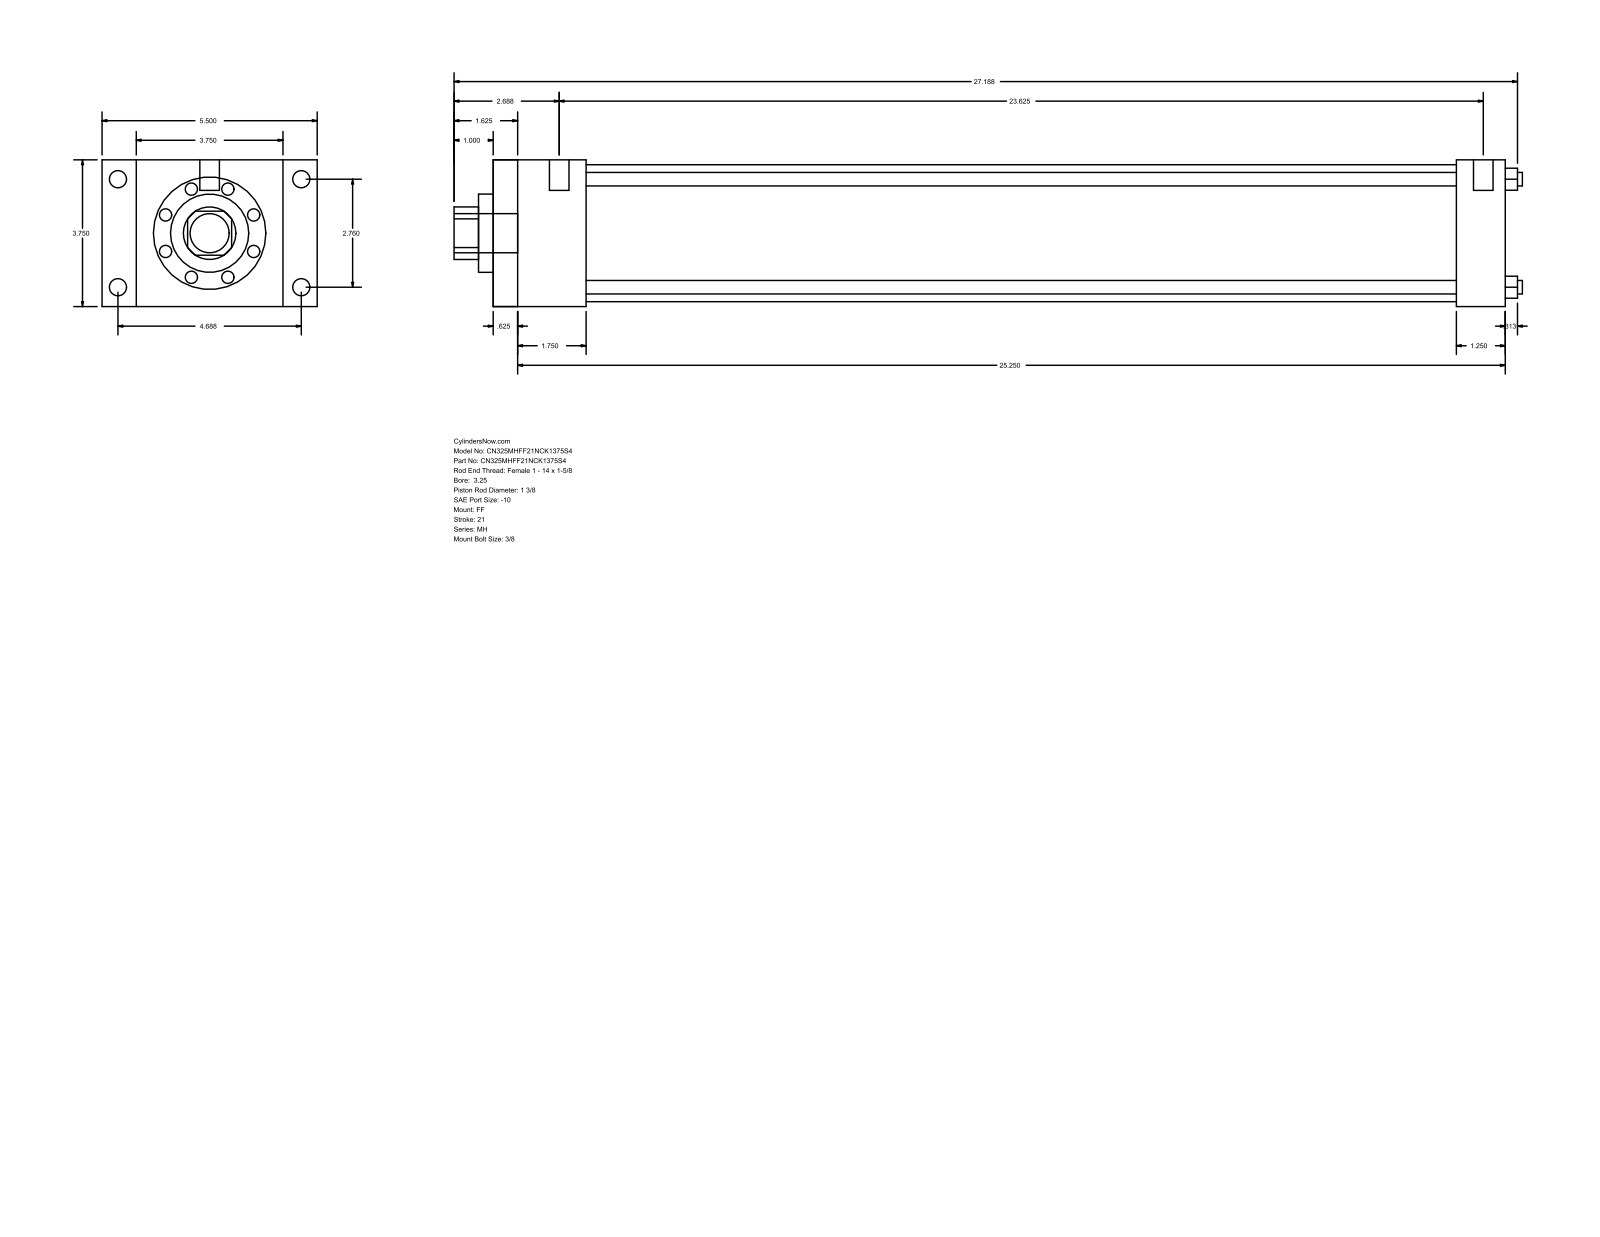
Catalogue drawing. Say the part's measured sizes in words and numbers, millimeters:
The part is named "MH_FF__0325_1.375". Its 3-D file was written by "GSSL Pune (CONFIG_CONTROL_DESIGN)". It is 0 solids with 92 faces: 64 planar, 28 cylindrical and 0 other. Overall it measures 693.74 by 139.7 by 95.25 millimeters. Round holes: 4 of diameter 8.76, 1 of diameter 34.92, 1 of diameter 50.8, 1 of diameter 88.9. Round bosses or shafts: 4 of diameter 11.13, 4 of diameter 5.56, 2 of diameter 12.7, 1 of diameter 25.4. Partial cylindrical surfaces (rounded edges, fillets, slot ends): 1 of radius 17.06. The main face-to-face distances are 95.24, 657.22, 15.87, 641.35, 22.23, 117.47, 625.48, 609.61, 31.74, 60.32. The hole center spacings are 49.57, 70.1, 99.14.
